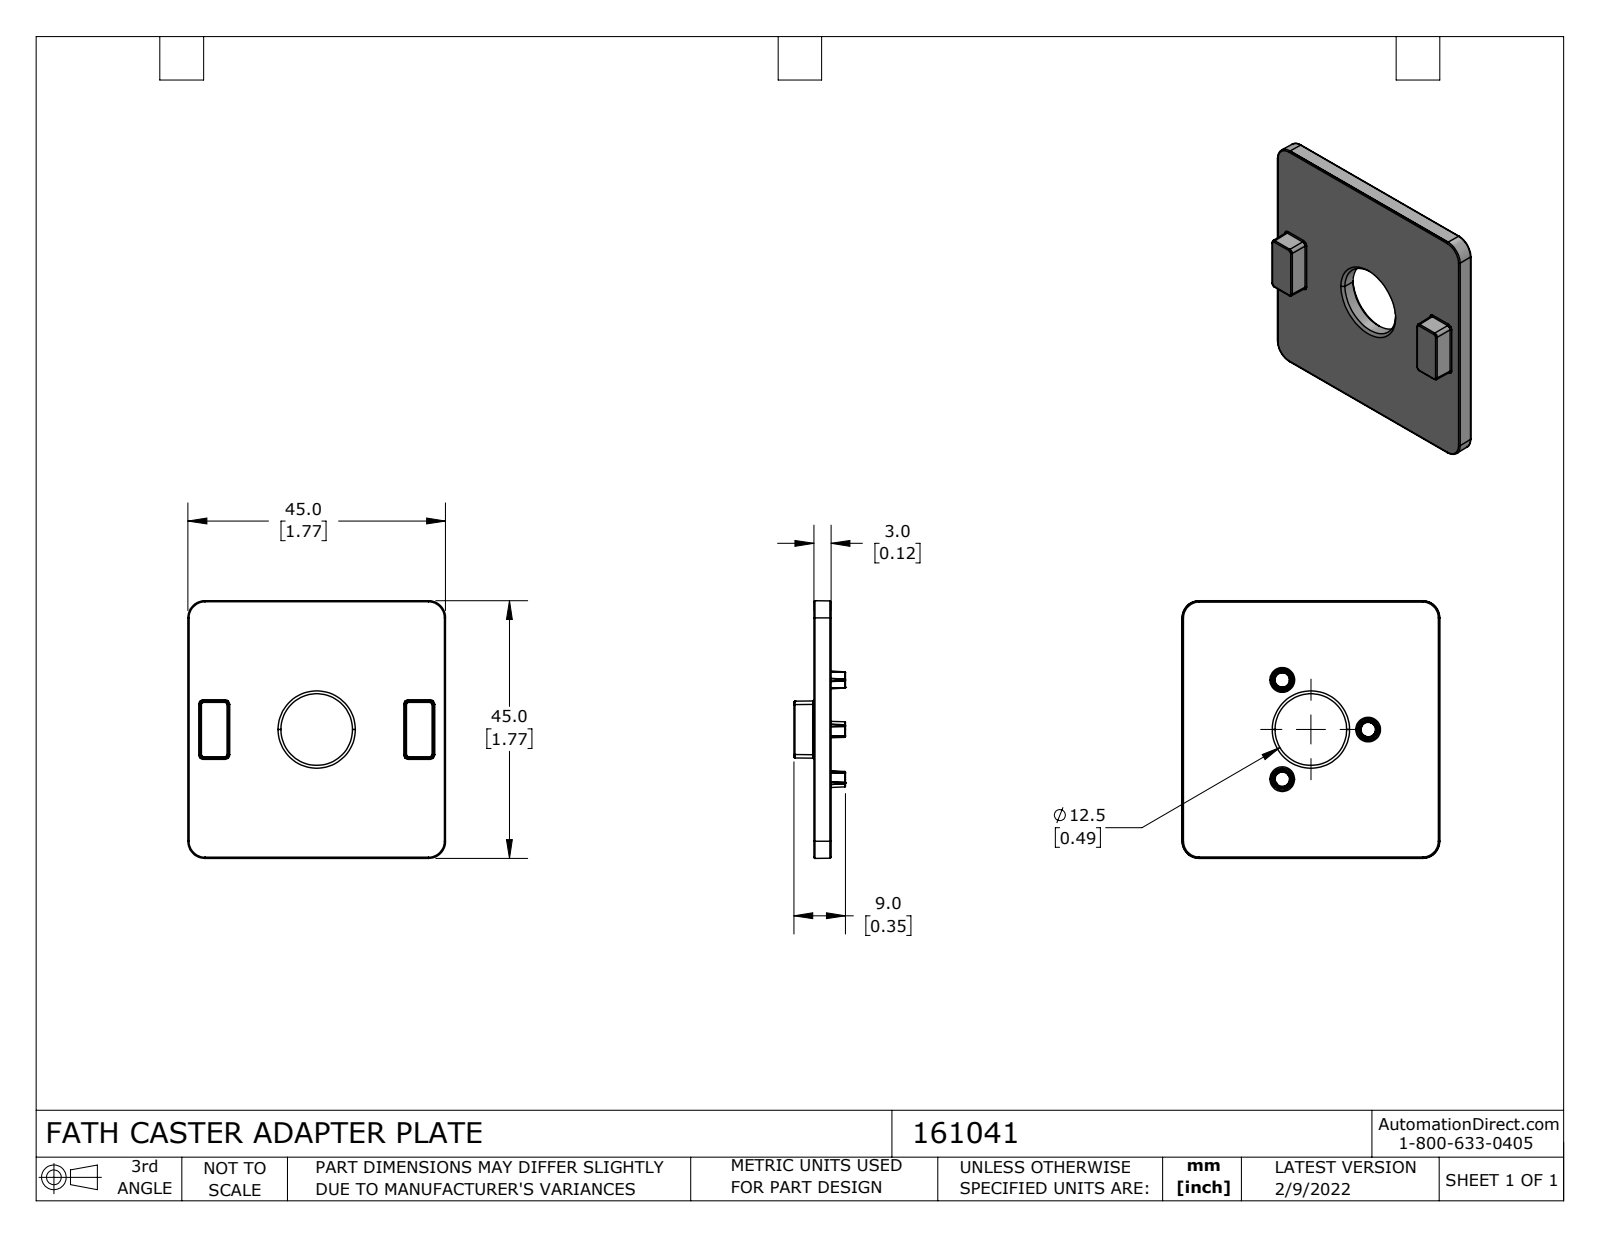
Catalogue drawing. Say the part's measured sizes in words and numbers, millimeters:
The part is named "161041". Its 3-D file was written by "SolidWorks 2021 (CONFIG_CONTROL_DESIGN)". It is 1 solid with 312 faces: 31 planar, 35 cylindrical and 246 other. Overall it measures 44.99 by 44.99 by 9 millimeters. Its volume is 6 038 cubic millimeters and its surface area 4 644 square millimeters. Round holes: 1 of diameter 12.5. Partial cylindrical surfaces (rounded edges, fillets, slot ends): 20 of radius 0.2, 8 of radius 0.6. The main face-to-face distances are 3, 6.5, 3.5, 42.9, 7.1, 35.8, 27.5, 2.5, 5.5, 9.
